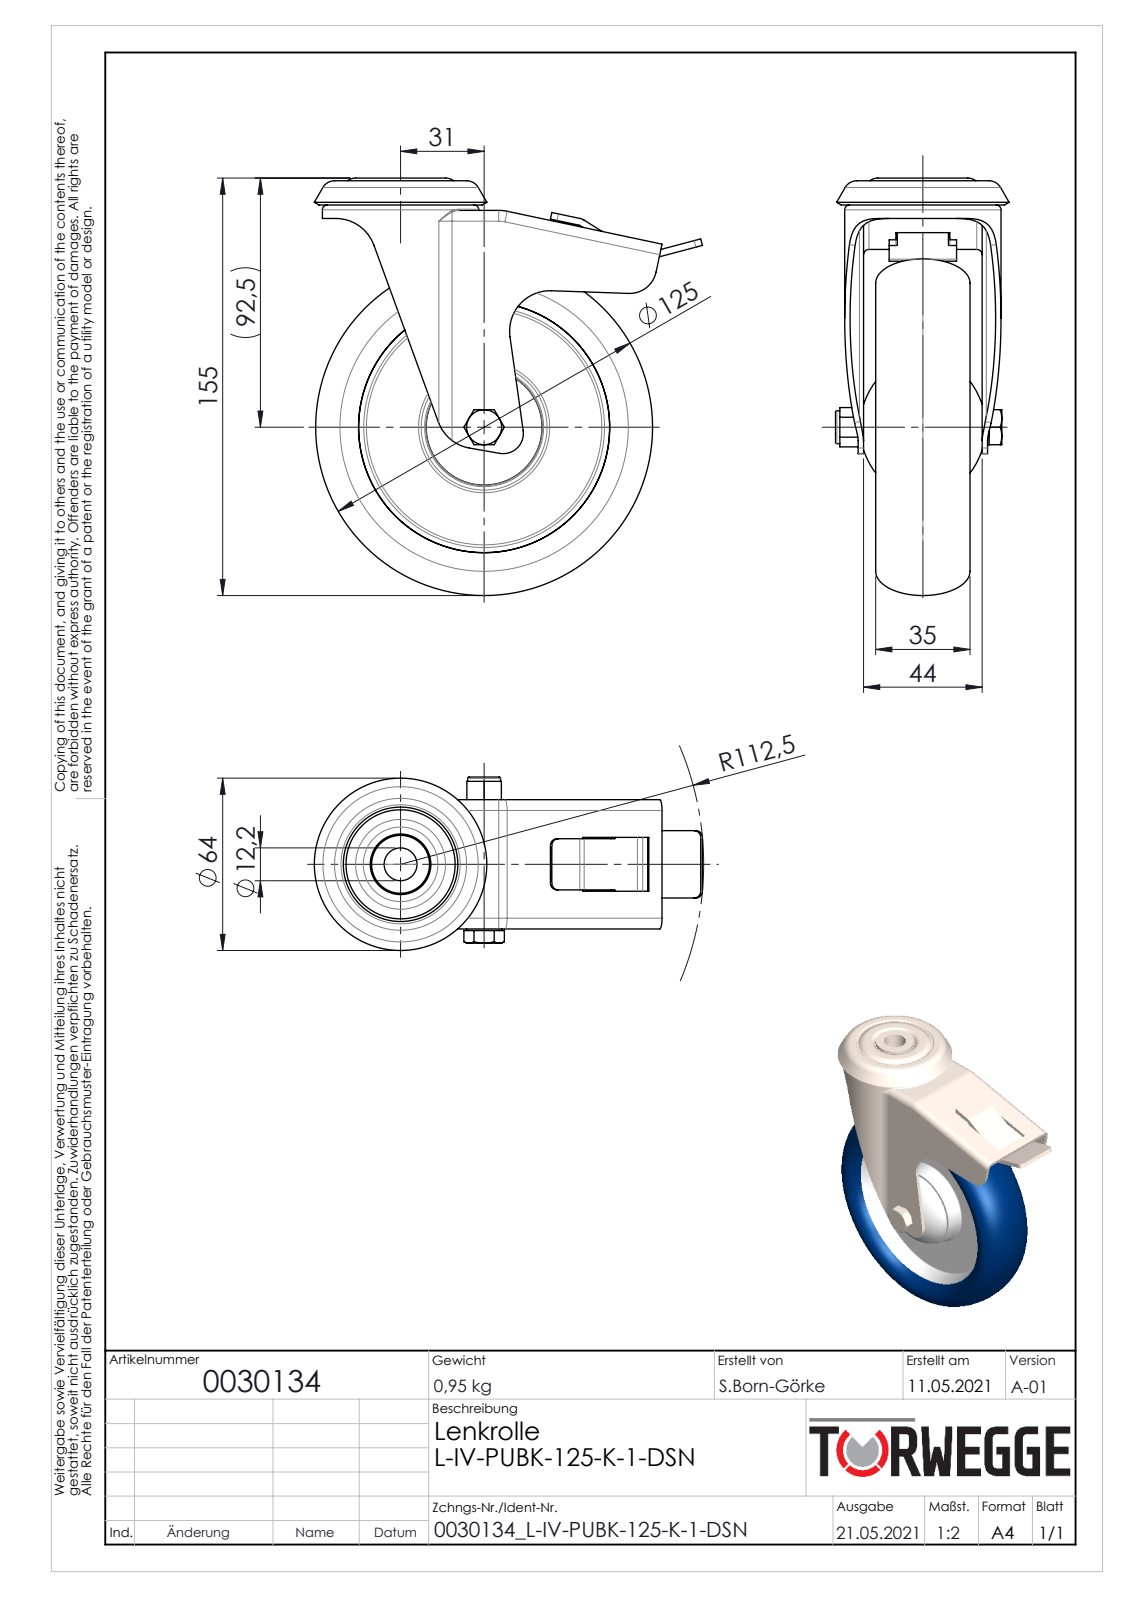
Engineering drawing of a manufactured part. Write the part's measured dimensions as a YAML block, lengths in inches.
part_name: "0030134"
step_written_by: "SolidWorks 2020 (AUTOMOTIVE_DESIGN)"
units: inches
bodies: {solids: 8, faces: 270, planar: 83, cylindrical: 75, other: 112}
overall_size: [6.102, 5.669, 2.535]
volume: 17.93
surface_area: 195.8
round_holes:
  - {diameter: 0.262, count: 1}
  - {diameter: 0.315, count: 1}
  - {diameter: 0.323, count: 1}
  - {diameter: 0.48, count: 1}
  - {diameter: 1.299, count: 1}
  - {diameter: 1.378, count: 1}
round_bosses_or_shafts:
  - {diameter: 1.142, count: 1}
  - {diameter: 0.846, count: 1}
  - {diameter: 0.591, count: 1}
  - {diameter: 0.512, count: 1}
  - {diameter: 0.48, count: 1}
partial_cylinders:
  - {radius: 0.098, count: 5}
  - {radius: 0.079, count: 4}
  - {radius: 0.157, count: 4}
  - {radius: 0.591, count: 4}
  - {radius: 0.394, count: 3}
  - {radius: 0.02, count: 2}
  - {radius: 0.197, count: 2}
  - {radius: 0.472, count: 2}
face_to_face_distances: [0.079, 0.846, 0.768, 0.965, 1.043, 1.811, 0.197, 1.732, 1.89, 0.522]
